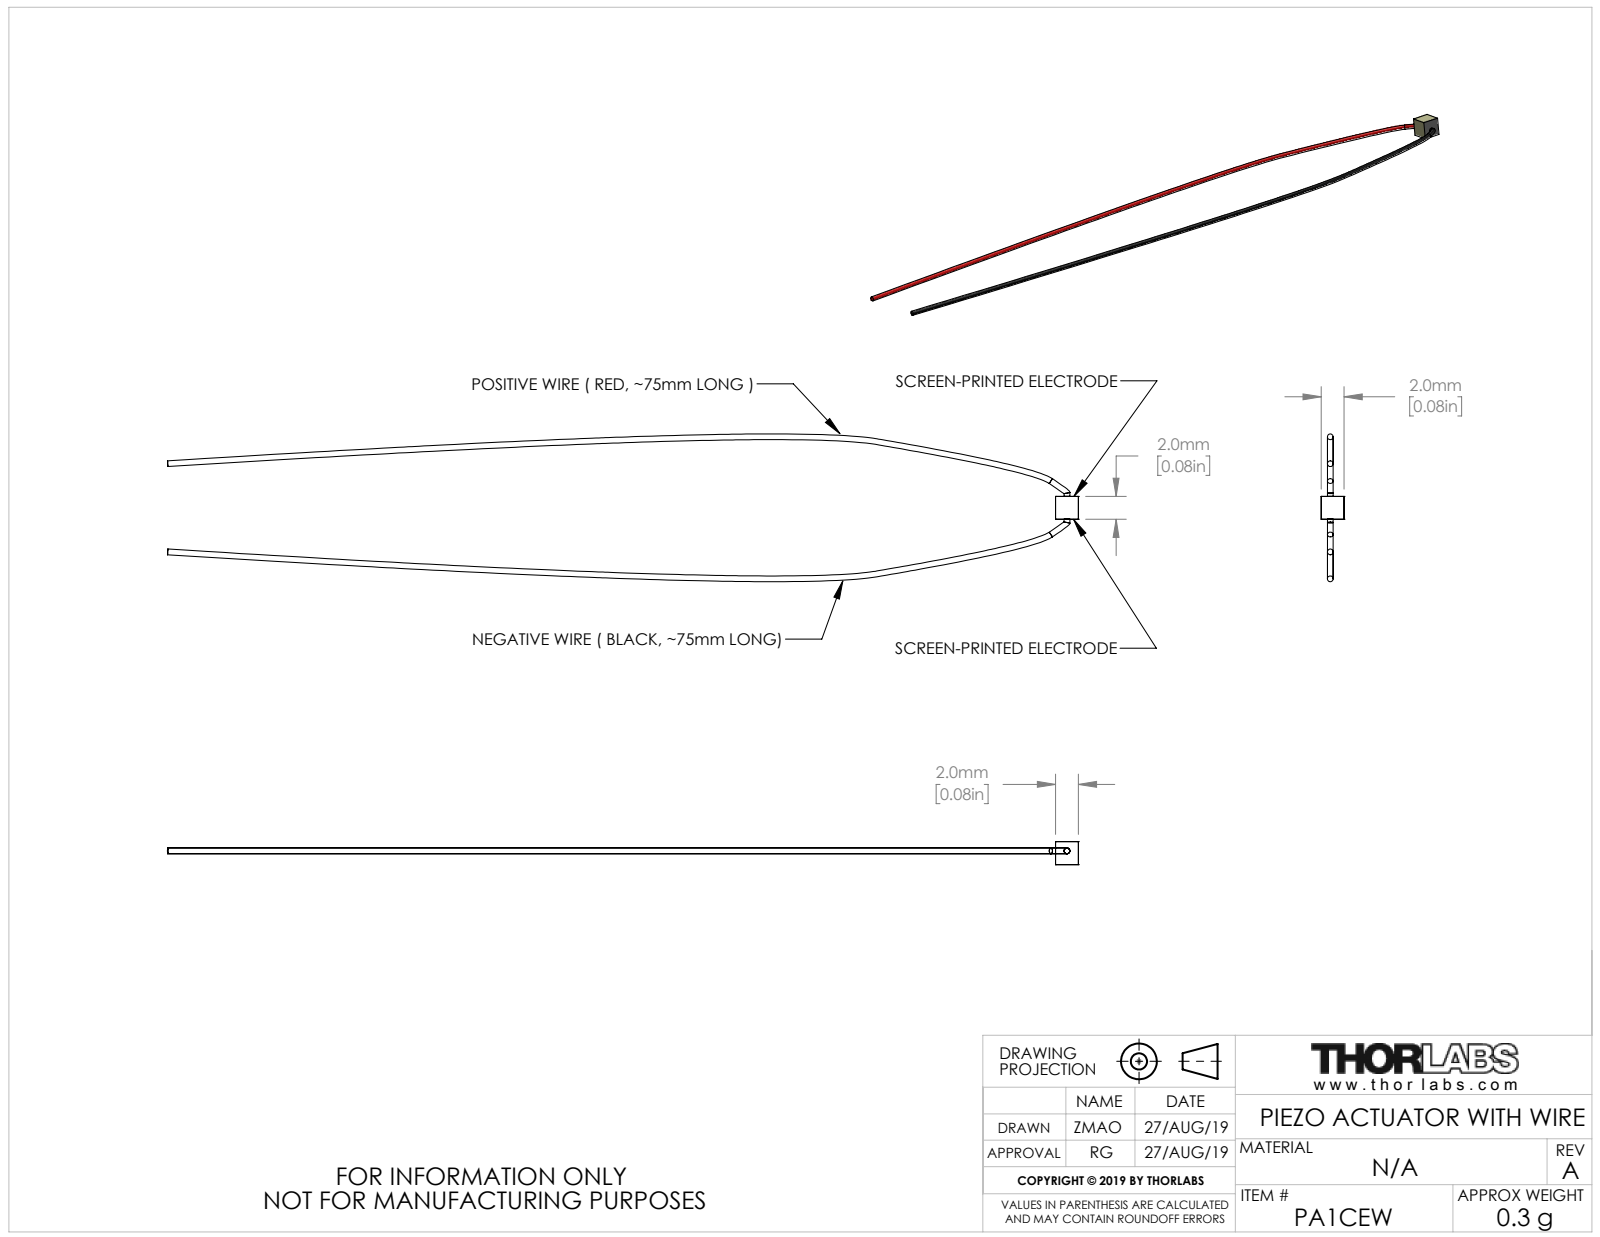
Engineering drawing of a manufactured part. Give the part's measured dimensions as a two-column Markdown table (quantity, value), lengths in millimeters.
| quantity | value |
| --- | --- |
| part name | CTN014517 |
| STEP written by | SolidWorks 2018 (AUTOMOTIVE_DESIGN) |
| units | millimeters |
| bodies | 1 solid, 20 faces (8 planar, 4 cylindrical, 8 other) |
| overall size | 79.53 × 12.9 × 2 |
| volume | 39 mm³ |
| surface area | 274 mm² |
| round bosses / shafts (diameter × count) | 0.5 × 1 |
| main face-to-face distances | 2 |
